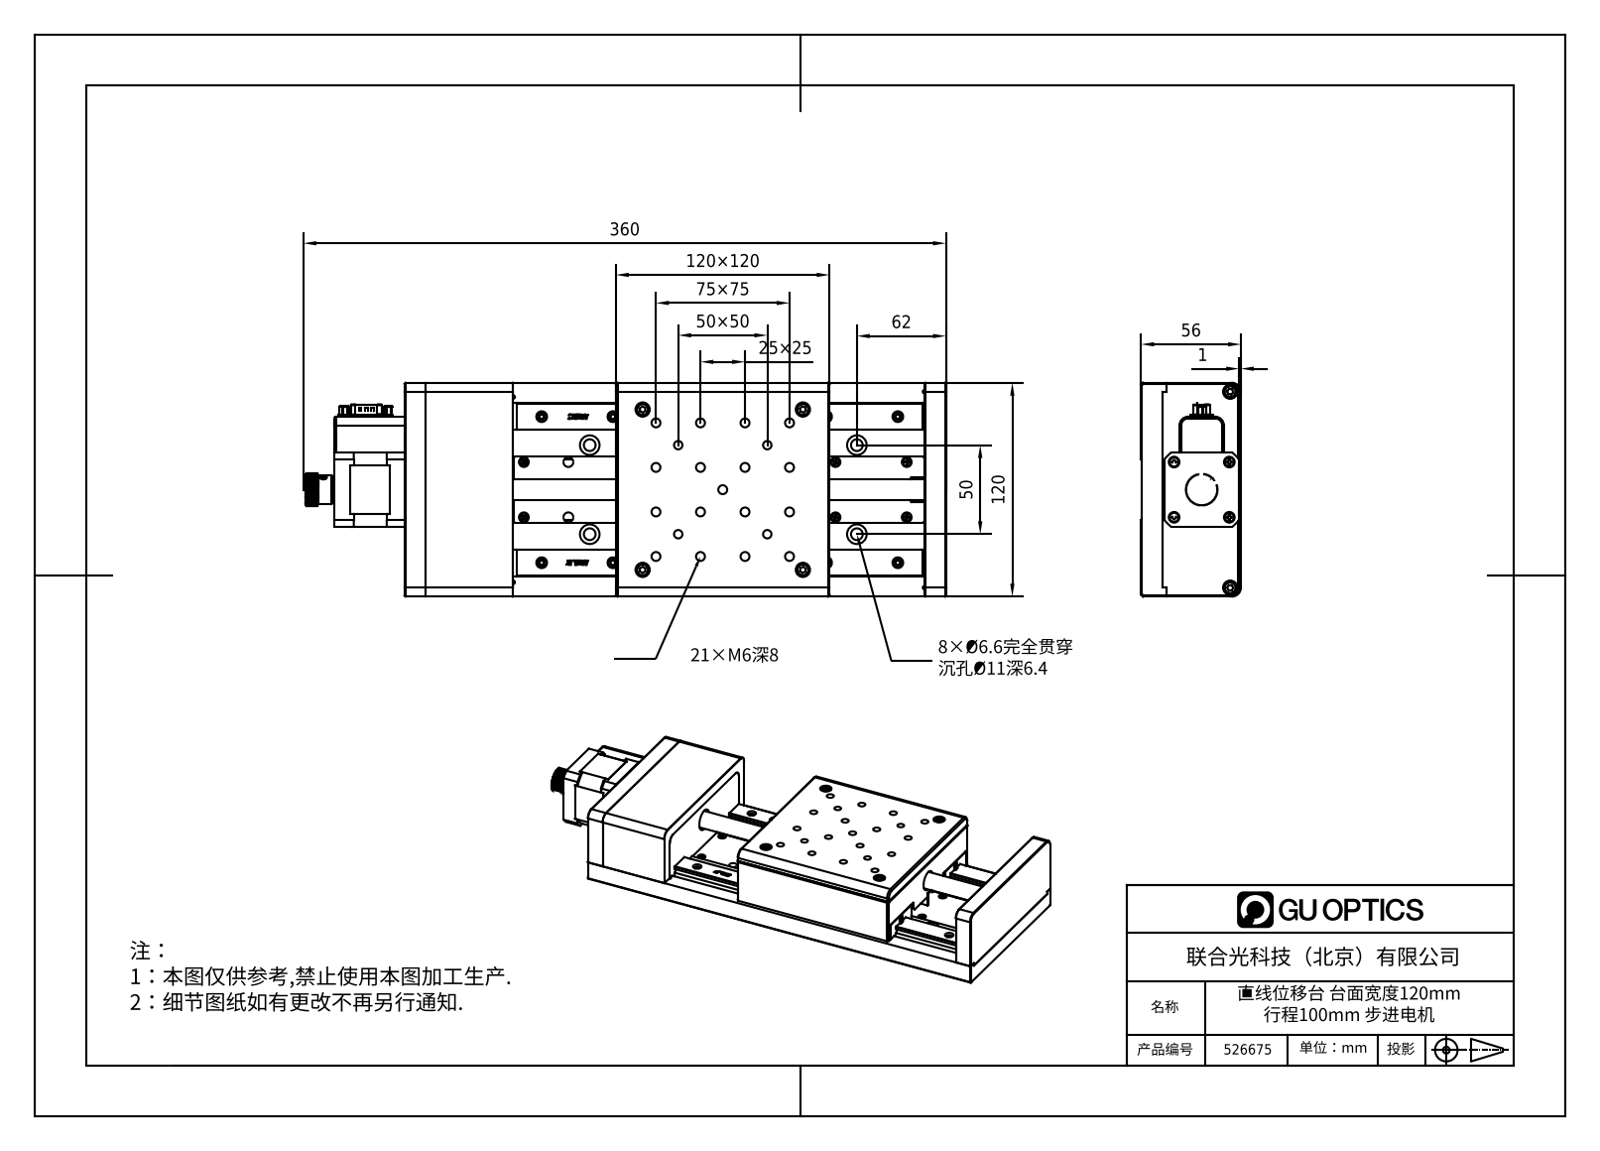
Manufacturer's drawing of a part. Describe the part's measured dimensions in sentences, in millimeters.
The part is named "FMS120-100". Its 3-D file was written by "SolidWorks 2017 (CONFIG_CONTROL_DESIGN)". It is 0 solids with 1157 faces: 586 planar, 354 cylindrical and 217 other. Overall it measures 359.6 by 120 by 56 millimeters. Round holes: 17 of diameter 5, 14 of diameter 8, 12 of diameter 6, 8 of diameter 6.6, 5 of diameter 2, 4 of diameter 4.71, 4 of diameter 11, 2 of diameter 2.5, 2 of diameter 4.5, 1 of diameter 3.3, 1 of diameter 14. Round bosses or shafts: 9 of diameter 1, 8 of diameter 4.4, 4 of diameter 5.5, 3 of diameter 7, 2 of diameter 4.2, 1 of diameter 16, 1 of diameter 12. Partial cylindrical surfaces (rounded edges, fillets, slot ends): 27 of radius 0.5, 15 of radius 1, 8 of radius 0.3, 7 of radius 0.4, 6 of radius 5, 4 of radius 1.5, 1 of radius 9, 1 of radius 20. The main face-to-face distances are 14, 28, 42, 56, 120, 13.7, 55.7, 12, 1, 42.2. The hole center spacings are 50, 25, 35.36, 70.71, 21.92, 31, 90, 100.
